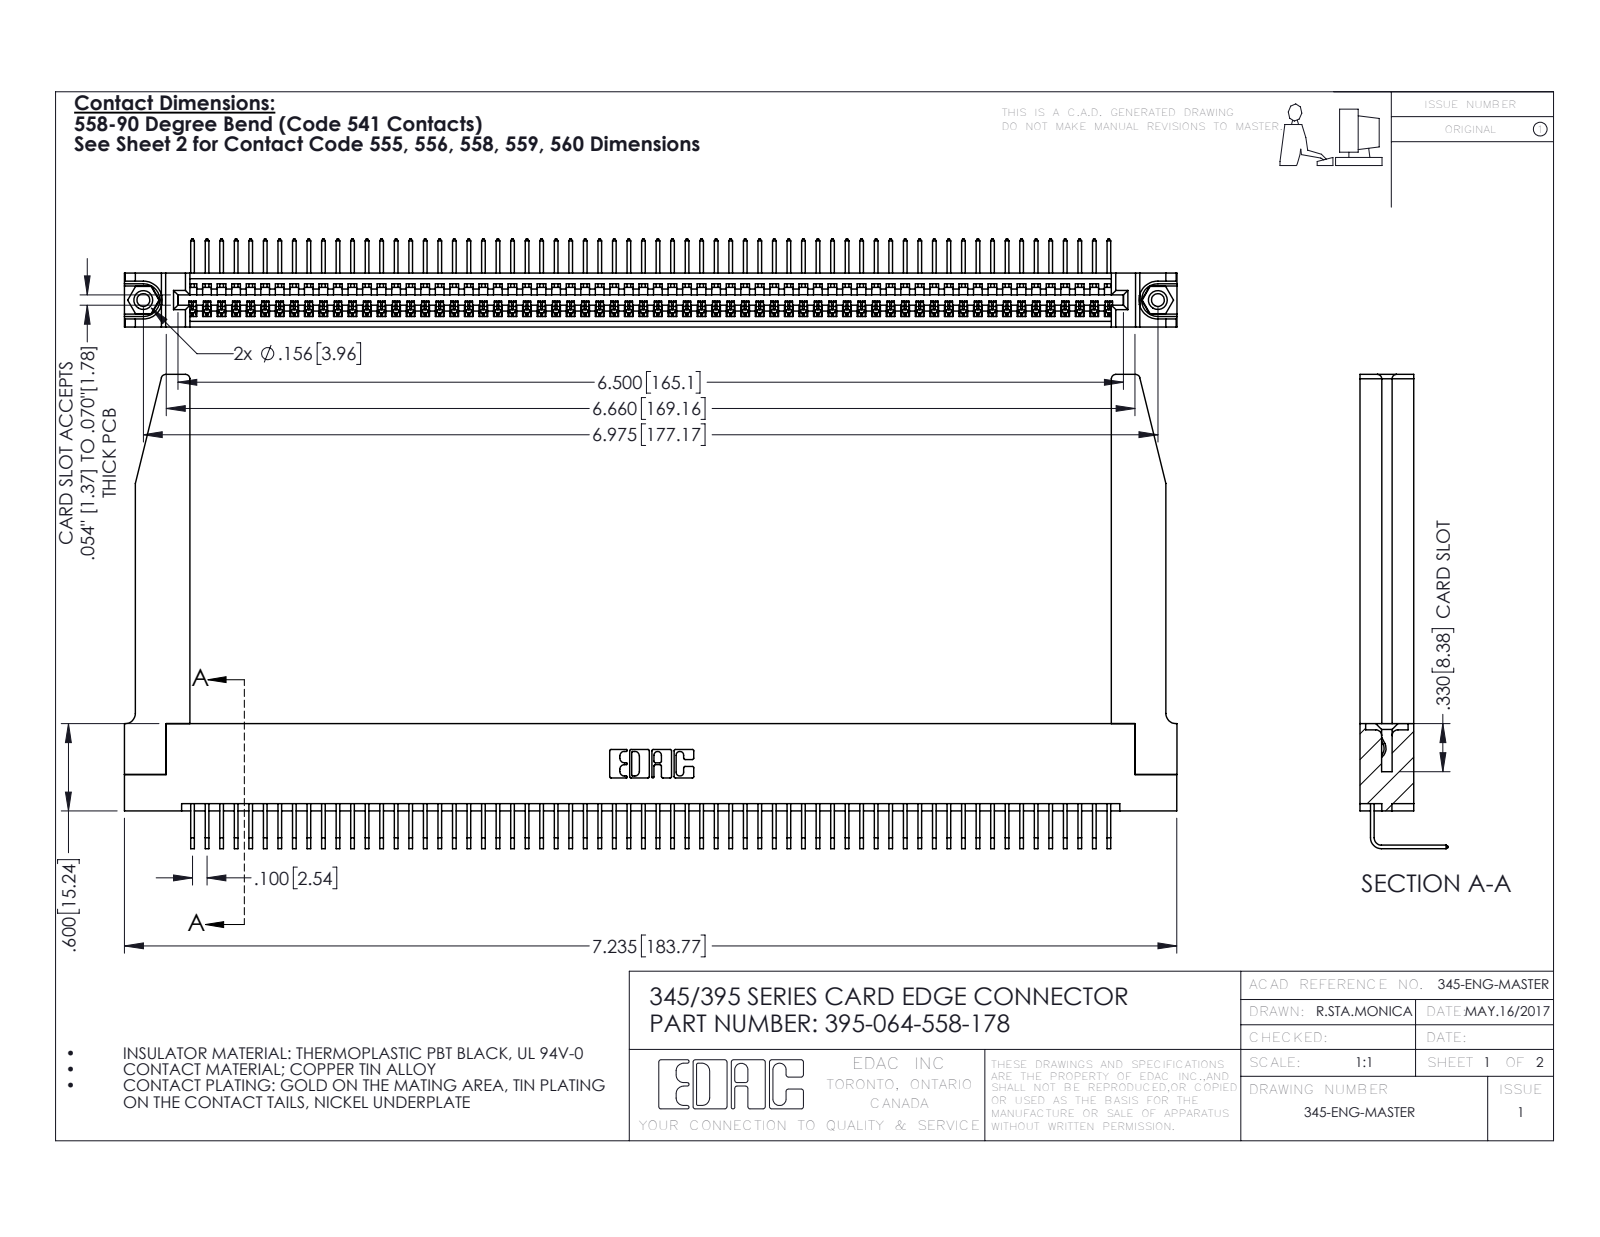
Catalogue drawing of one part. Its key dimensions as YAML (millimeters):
part_name: "345 Part_Flush Mounting Lugs - 0.156 Dia-TH; 345-250-001_345-250-001-102; 345-292-001_558 Tail - 2; 345-220-078_345-220-078 (+1 more)"
step_written_by: "SolidWorks 2016 (CONFIG_CONTROL_DESIGN)"
units: millimeters
bodies: {solids: 69, faces: 4200, planar: 2910, cylindrical: 1238, other: 52}
overall_size: [183.8, 82.8, 15.4]
volume: 25610
surface_area: 32120
round_holes:
  - {diameter: 2.3, count: 2}
  - {diameter: 3.2, count: 2}
  - {diameter: 4, count: 2}
  - {diameter: 1.6, count: 1}
round_bosses_or_shafts:
  - {diameter: 3.9, count: 2}
partial_cylinders:
  - {radius: 0.2, count: 128}
  - {radius: 0.3, count: 22}
  - {radius: 0.8, count: 8}
  - {radius: 0.2, count: 6}
  - {radius: 0.8, count: 6}
  - {radius: 0.7, count: 3}
  - {radius: 0.8, count: 2}
  - {radius: 1, count: 2}
face_to_face_distances: [1.8, 9.4, 7.6, 5.1, 2.5, 6.9, 0.6, 5.7, 3.8, 3.8]
hole_center_spacings: [6.9, 171.2, 177.2]
